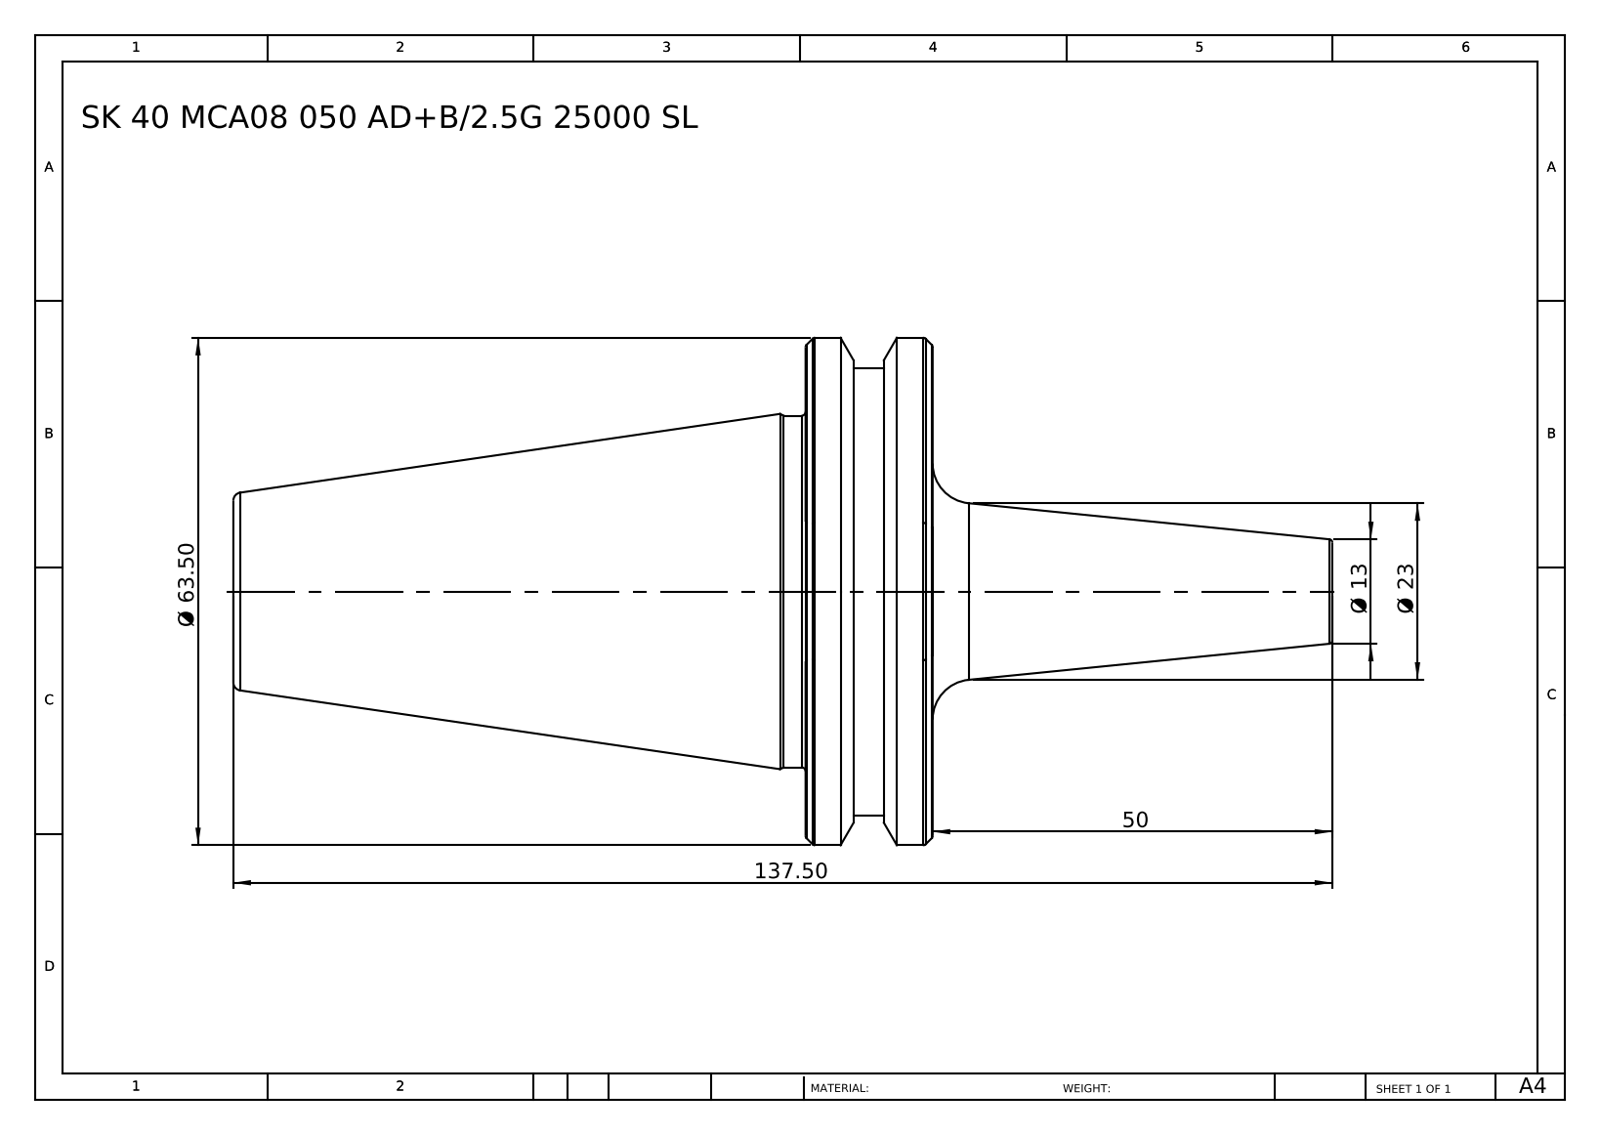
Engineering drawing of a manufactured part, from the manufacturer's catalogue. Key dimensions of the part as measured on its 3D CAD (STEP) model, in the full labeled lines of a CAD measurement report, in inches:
Part name (STEP PRODUCT): SK 40 MCA08 050 AD+B-2.5G 25000 SL
STEP written by: SolidWorks 2014 (CONFIG_CONTROL_DESIGN)
Units: inches
Bodies: 1 solid, 64 faces (6 planar, 8 cylindrical, 50 other)
Overall size (bounding box): 5.413 × 2.5 × 2.5
Volume: 7.962 in³ · Surface area: 30.02 in²
Round bosses / shafts (diameter × count): ⌀2.5 ×1, ⌀2.205 ×1, ⌀1.732 ×1
Main face-to-face distances: 0.626, 3.445, 2.819, 0.24, 0.386, 3.205, 0.39, 0.15, 0.236, 3.055
